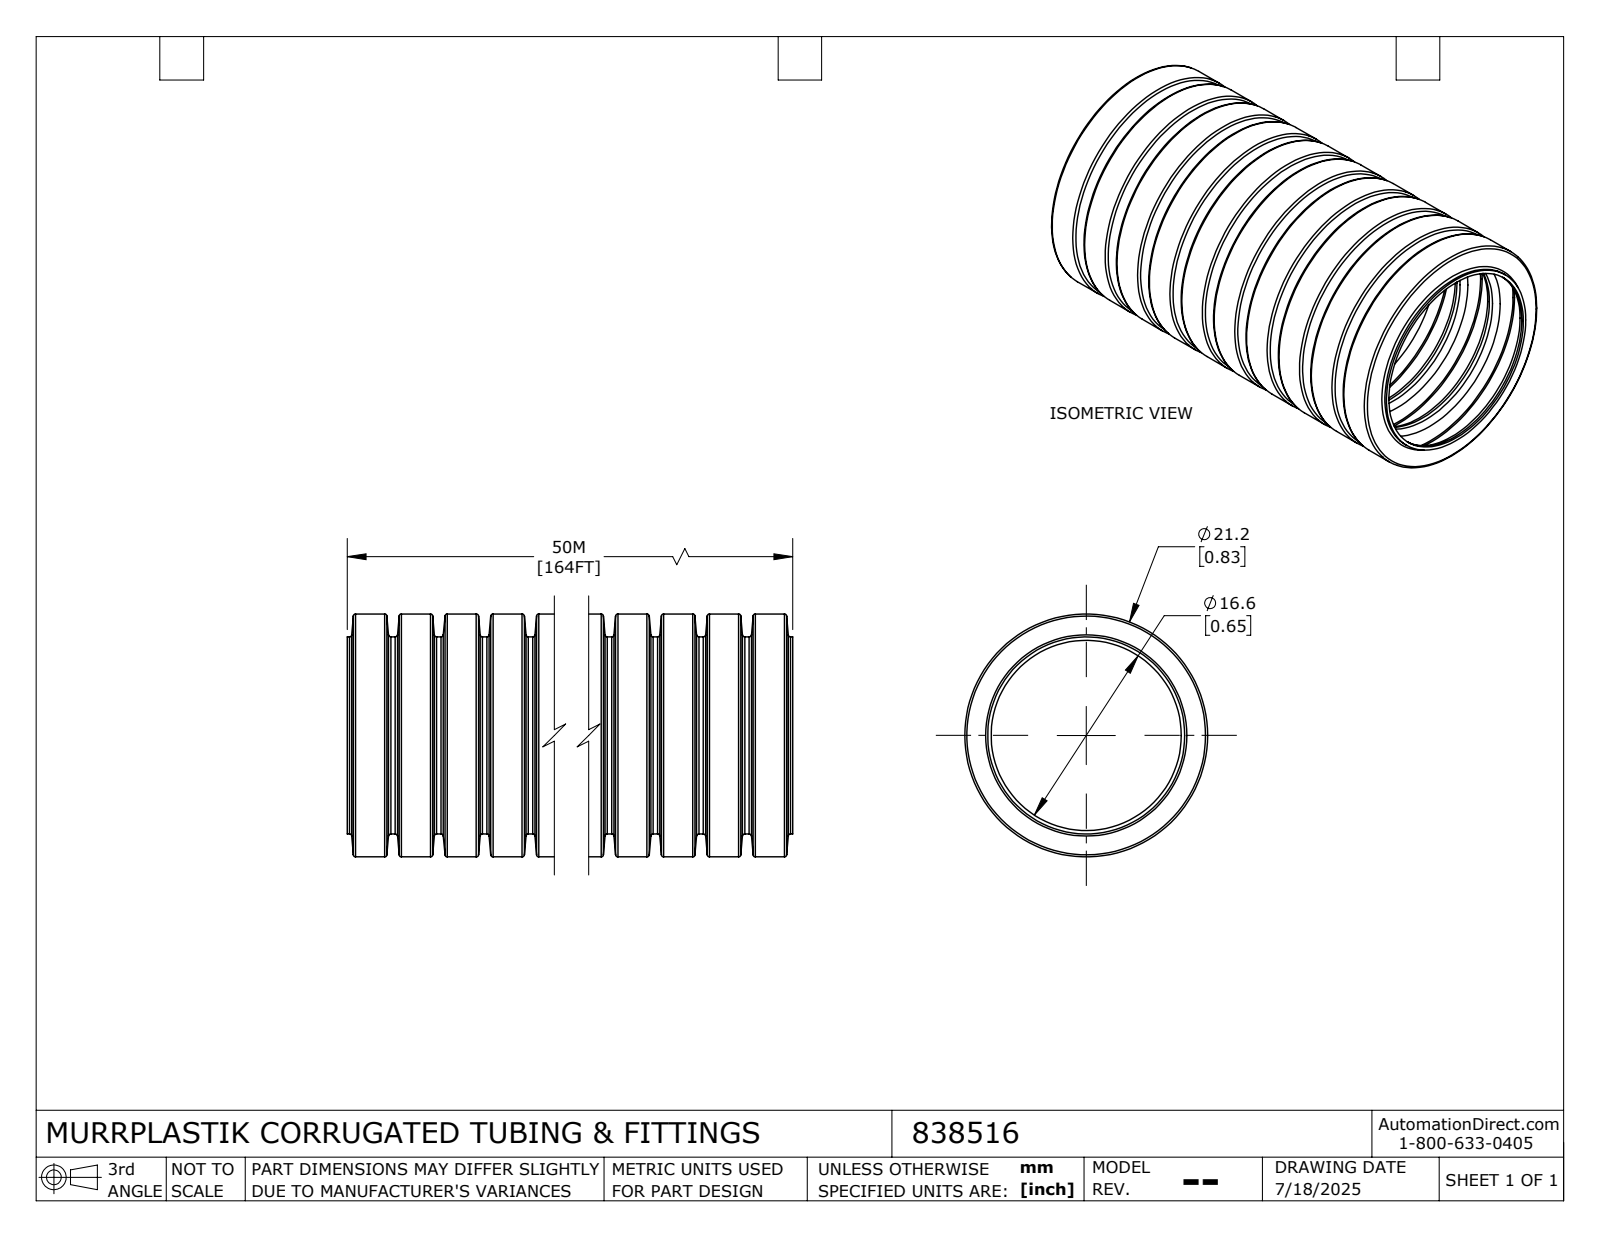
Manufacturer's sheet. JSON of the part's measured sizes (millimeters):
{"part_name": "838516_Default", "step_written_by": "SolidWorks 2024 (CONFIG_CONTROL_DESIGN)", "units": "millimeters", "bodies": {"solids": 1, "faces": 164, "planar": 2, "cylindrical": 42, "other": 120}, "overall_size": [40, 21.2, 21.2], "volume_mm3": 1350, "surface_area_mm2": 8942, "round_holes": [[16.6, 1], [20.6, 1]], "round_bosses_or_shafts": [[21.2, 1], [17.2, 1]], "face_to_face_distances": [40]}
